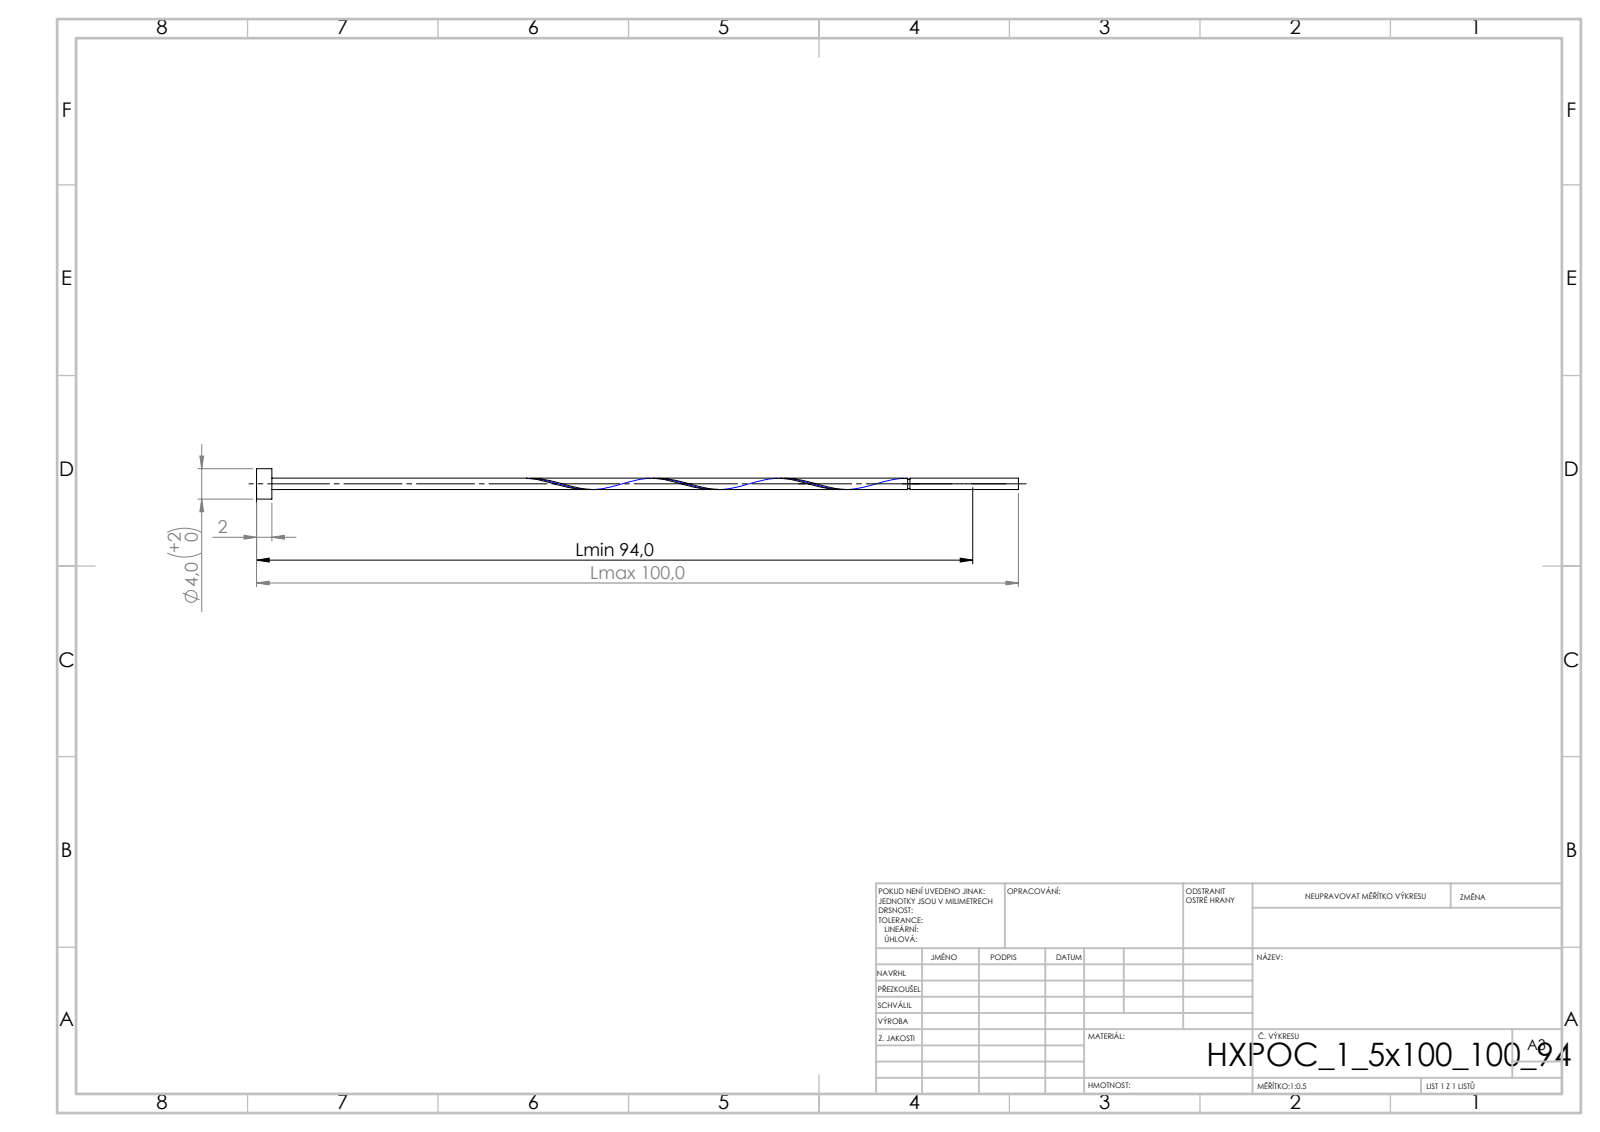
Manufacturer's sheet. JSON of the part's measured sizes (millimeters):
{"step_written_by": "SolidWorks 2019 (CONFIG_CONTROL_DESIGN)", "units": "millimeters", "bodies": {"solids": 1, "faces": 16, "planar": 6, "cylindrical": 9, "other": 1}, "overall_size": [100, 4, 4], "volume_mm3": 236, "surface_area_mm2": 678, "round_bosses_or_shafts": [[4, 1], [1.5, 1], [1.2, 1]], "face_to_face_distances": [2, 100, 98, 85.76, 83.76, 14.24, 85.46, 83.46, 14.54, 35.46]}
